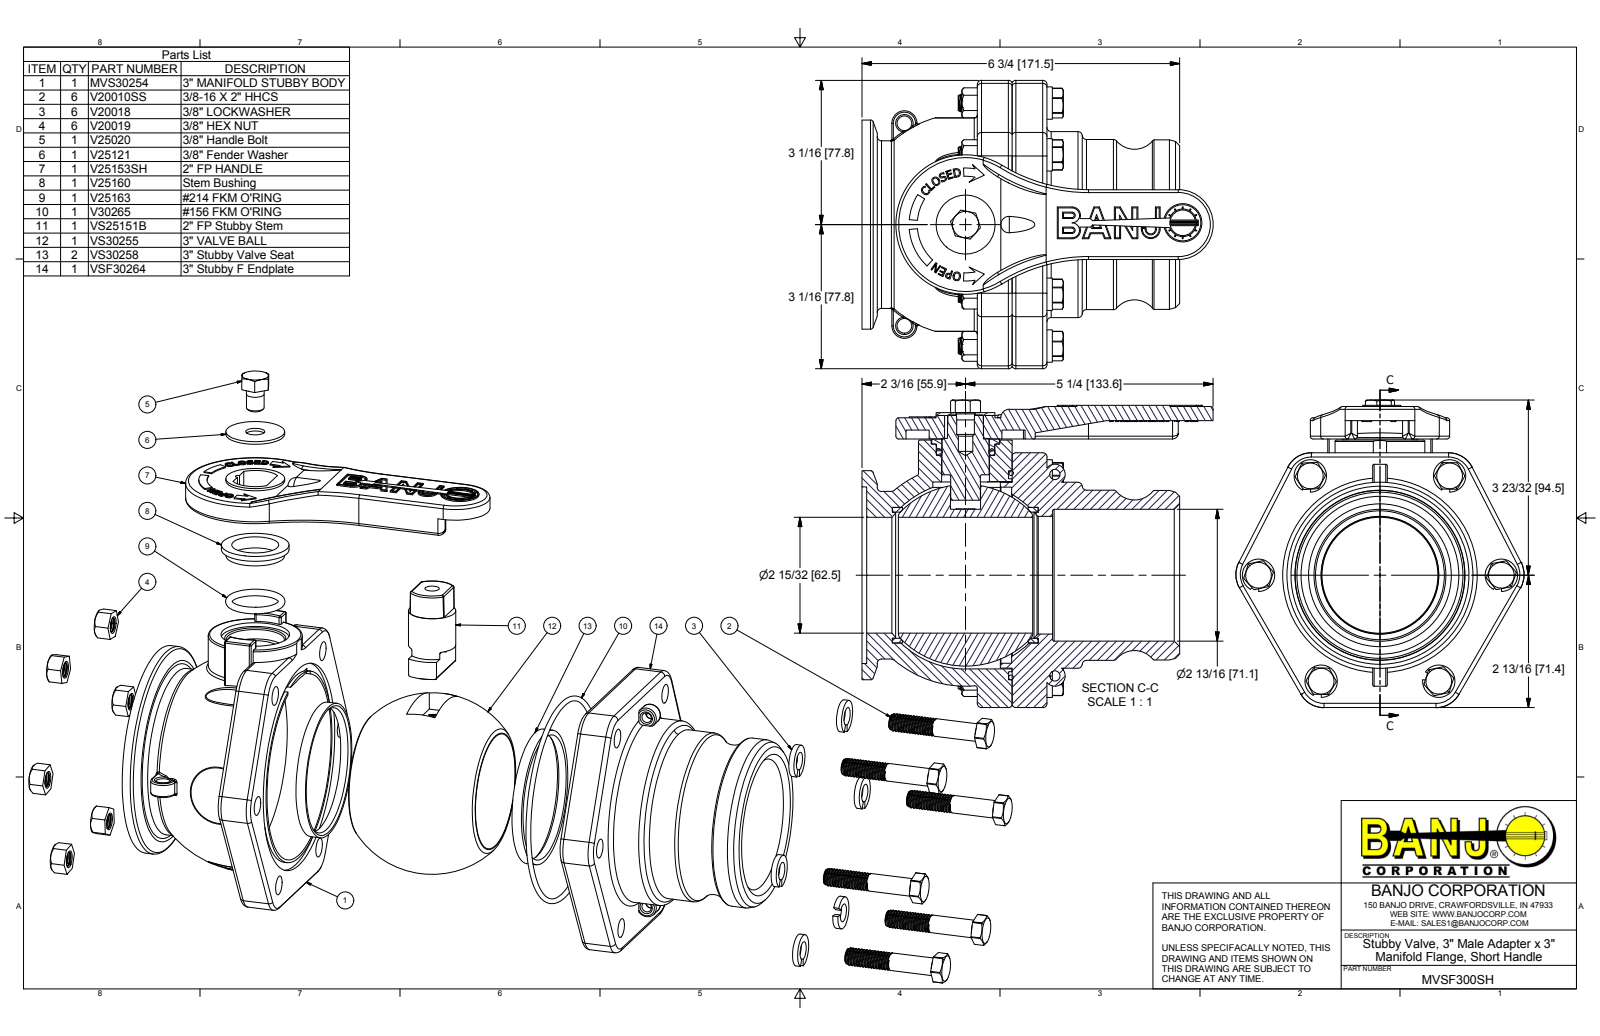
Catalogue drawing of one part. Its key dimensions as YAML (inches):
part_name: "VSF30264X; VSF30264Y; VSF30264; MVS30254X (+8 more)"
step_written_by: "Autodesk Inventor 2015 (AUTOMOTIVE_DESIGN)"
units: inches
bodies: {solids: 30, faces: 2839, planar: 1157, cylindrical: 776, other: 906}
overall_size: [7.46, 6.532, 6.124]
volume: 71.28
surface_area: 430.1
round_holes:
  - {diameter: 0.406, count: 7}
  - {diameter: 0.307, count: 6}
  - {diameter: 0.385, count: 6}
  - {diameter: 0.218, count: 2}
  - {diameter: 0.31, count: 2}
  - {diameter: 0.307, count: 1}
  - {diameter: 0.544, count: 1}
  - {diameter: 0.77, count: 1}
  - {diameter: 1, count: 1}
  - {diameter: 1.016, count: 1}
  - {diameter: 1.24, count: 1}
  - {diameter: 1.46, count: 1}
round_bosses_or_shafts:
  - {diameter: 0.324, count: 90}
  - {diameter: 0.375, count: 7}
  - {diameter: 0.687, count: 6}
  - {diameter: 4.44, count: 1}
  - {diameter: 4.098, count: 1}
  - {diameter: 3.95, count: 1}
  - {diameter: 3.945, count: 1}
  - {diameter: 3.613, count: 1}
partial_cylinders:
  - {radius: 0.09, count: 24}
  - {radius: 0.03, count: 16}
  - {radius: 0.162, count: 12}
  - {radius: 0.06, count: 8}
  - {radius: 0.032, count: 6}
  - {radius: 0.32, count: 6}
  - {radius: 0.56, count: 6}
  - {radius: 0.563, count: 6}
face_to_face_distances: [0.74, 1.48, 3.09, 3.83, 2.35, 0.1, 2.45, 3.19, 3.93, 0.69]
hole_center_spacings: [2.38, 2.513, 2.574, 2.577, 2.58, 2.614, 4.366, 4.442]
